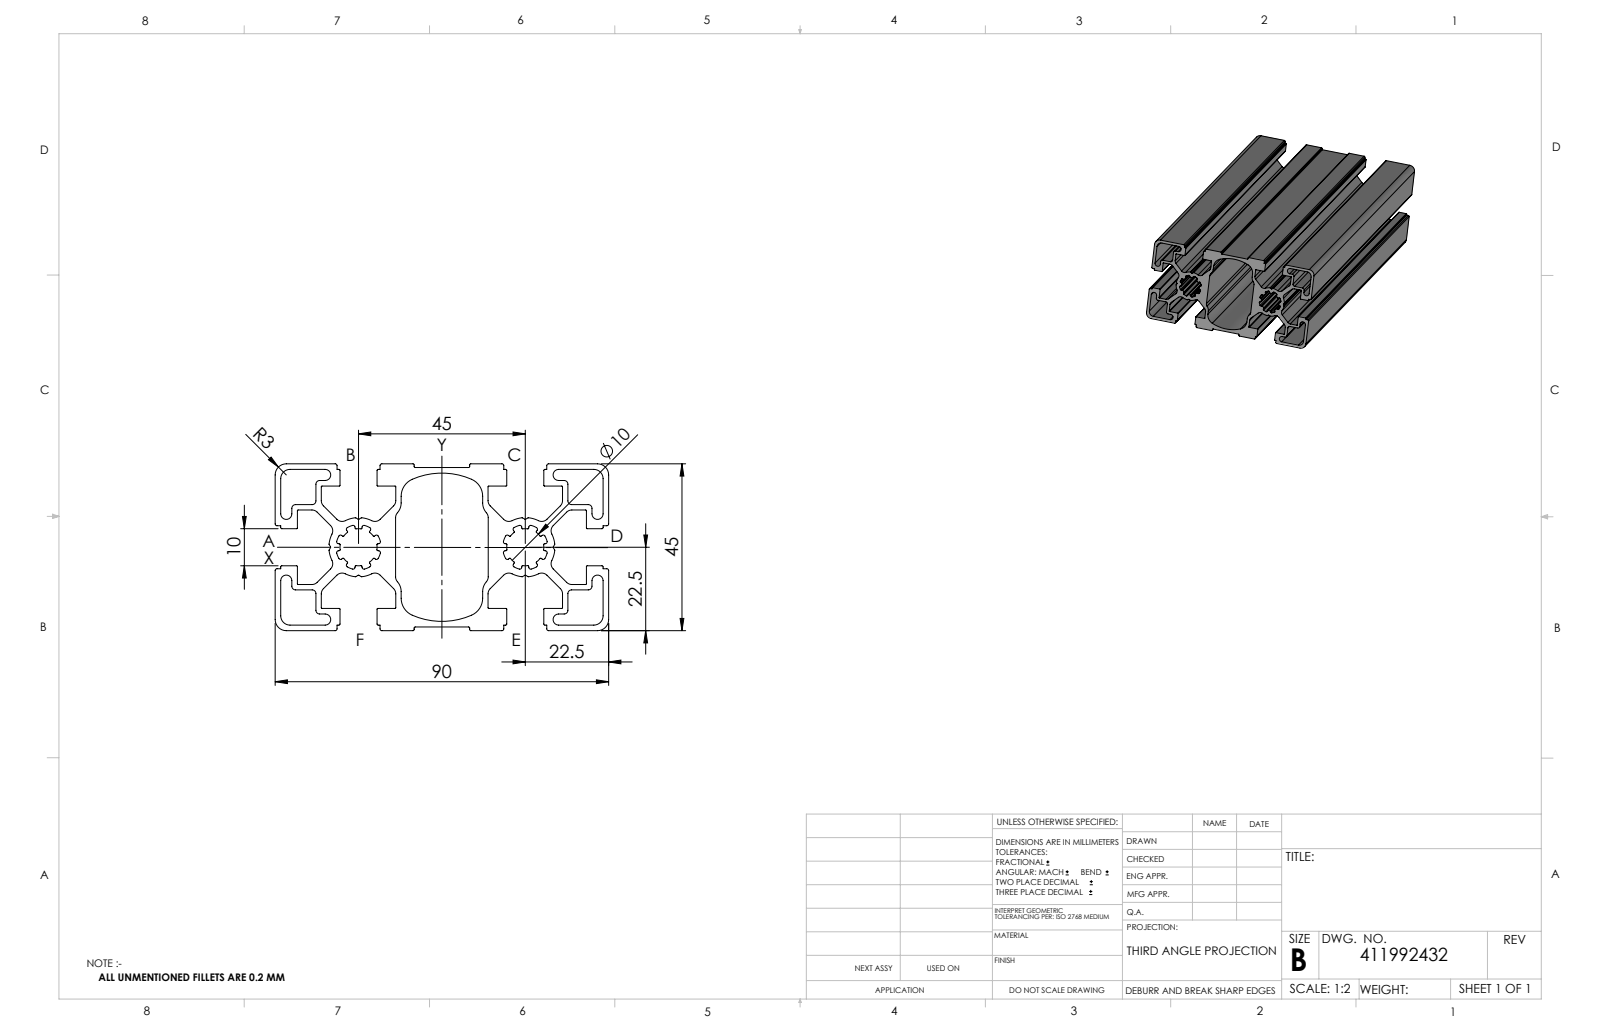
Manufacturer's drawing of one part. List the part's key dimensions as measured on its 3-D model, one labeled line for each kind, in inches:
Part name (STEP PRODUCT): 411992432_c_1
STEP written by: SolidWorks 2014 (CONFIG_CONTROL_DESIGN)
Units: inches
Bodies: 1 solid, 445 faces (166 planar, 279 cylindrical, 0 other)
Overall size (bounding box): 7.874 × 3.543 × 1.772
Volume: 13.78 in³ · Surface area: 295.2 in²
Partial cylindrical surfaces — rounded edges, fillets, slot ends (radius × count): R0.008 ×74, R0.02 ×44, R0.079 ×28, R0.012 ×20, R0.039 ×12, R0.059 ×8, R0.197 ×6, R0.098 ×4
Main face-to-face distances: 0.059, 1.772, 0.197, 0.177, 1.28, 0.236, 0.65, 0.846, 0.256, 0.199
